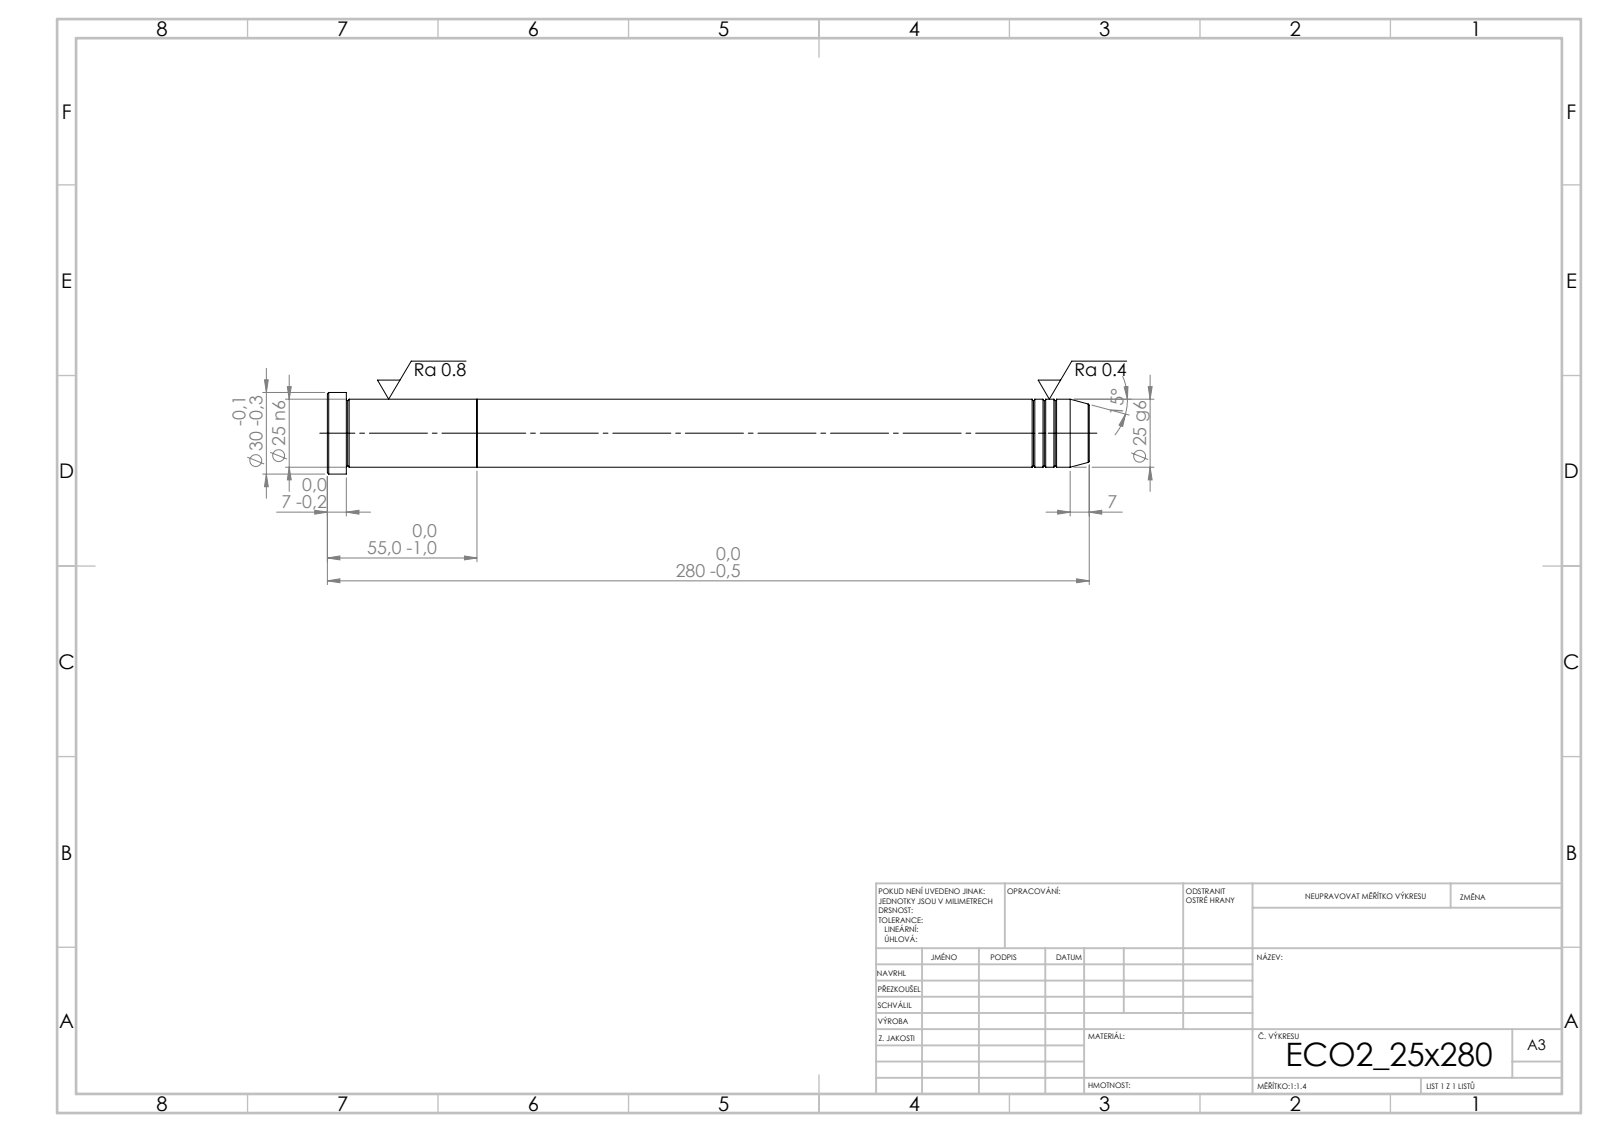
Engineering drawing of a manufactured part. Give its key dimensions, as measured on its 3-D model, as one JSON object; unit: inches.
{"step_written_by": "SolidWorks 2019 (CONFIG_CONTROL_DESIGN)", "units": "inches", "bodies": {"solids": 2, "faces": 39, "planar": 5, "cylindrical": 12, "other": 22}, "overall_size": [11.024, 1.181, 1.181], "volume_in3": 8.442, "surface_area_in2": 37.93, "round_bosses_or_shafts": [[1.181, 1], [0.984, 1]], "face_to_face_distances": [2.165, 8.858, 11.024, 10.748, 1.89, 0.276]}
